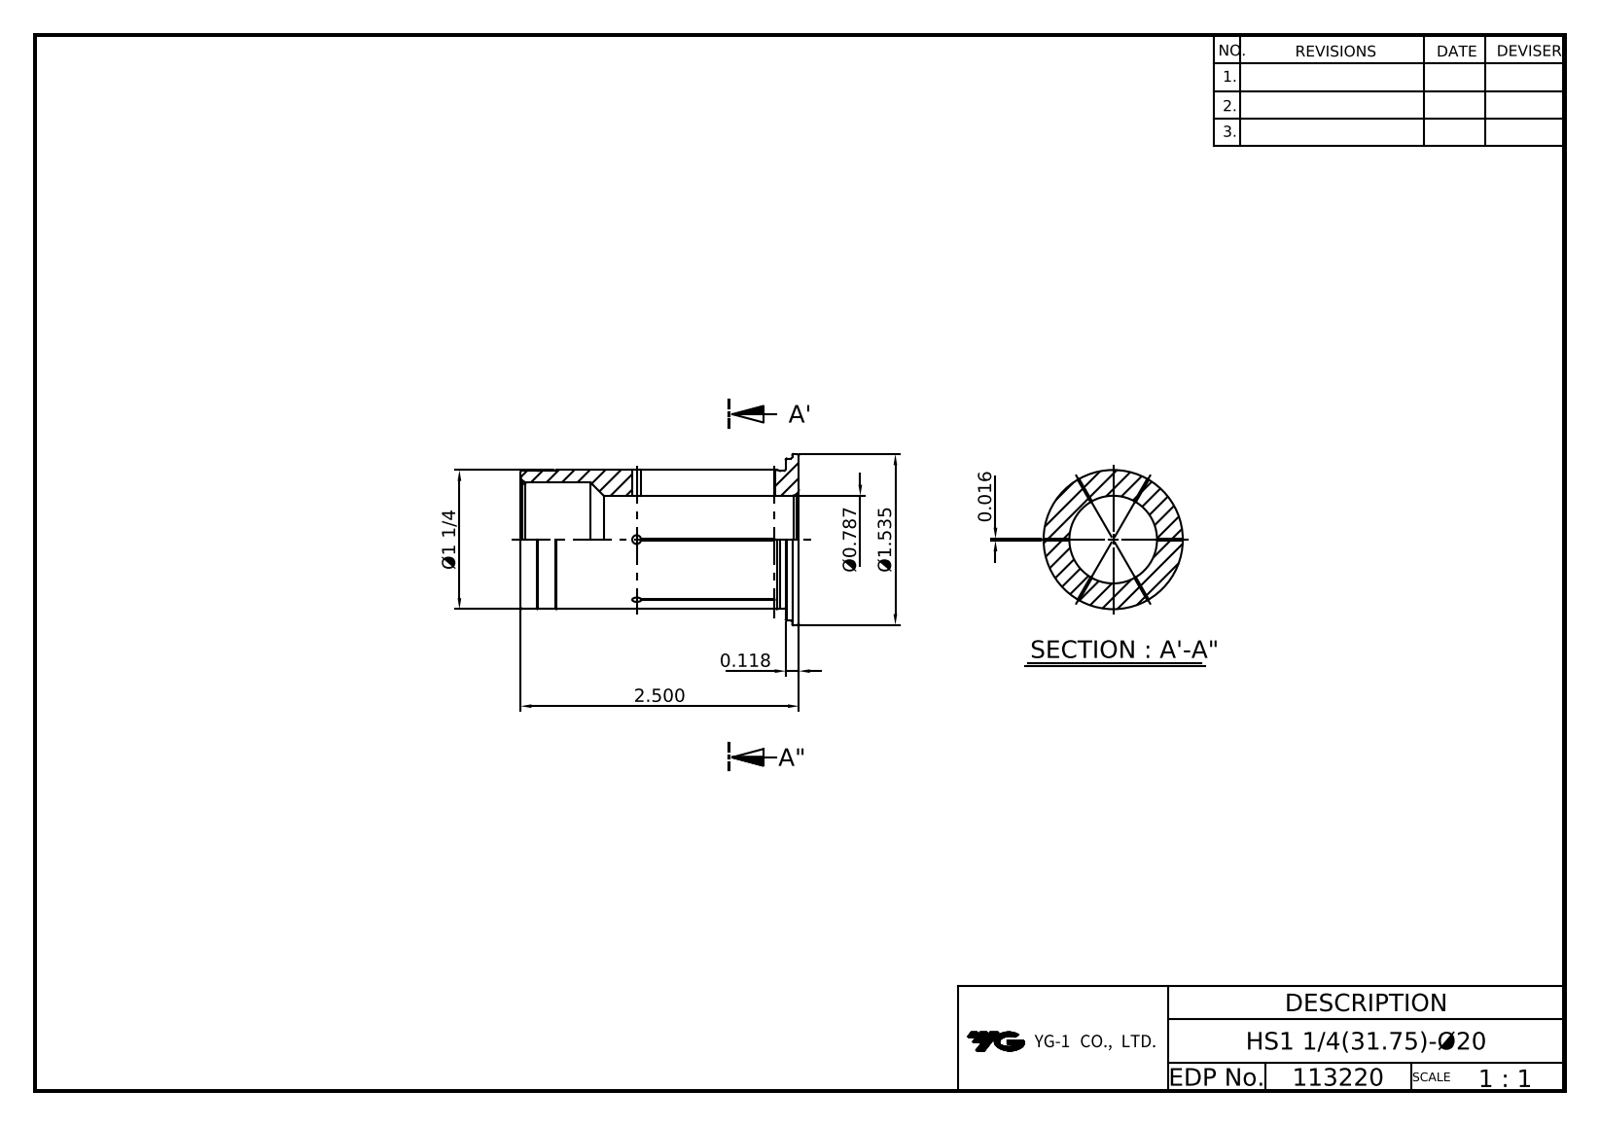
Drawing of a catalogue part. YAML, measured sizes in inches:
part_name: "LO-HS31.75-20"
step_written_by: "Autodesk Inventor 2022 (AUTOMOTIVE_DESIGN)"
units: inches
bodies: {solids: 1, faces: 29, planar: 4, cylindrical: 8, other: 17}
overall_size: [2.5, 1.535, 1.535]
volume: 1.669
surface_area: 18.86
round_holes:
  - {diameter: 0.787, count: 1}
  - {diameter: 1.024, count: 1}
round_bosses_or_shafts:
  - {diameter: 1.535, count: 1}
  - {diameter: 1.457, count: 1}
  - {diameter: 1.25, count: 1}
  - {diameter: 1.246, count: 1}
  - {diameter: 1.234, count: 1}
face_to_face_distances: [0.118, 0.059, 2.382, 2.5, 2.441]
